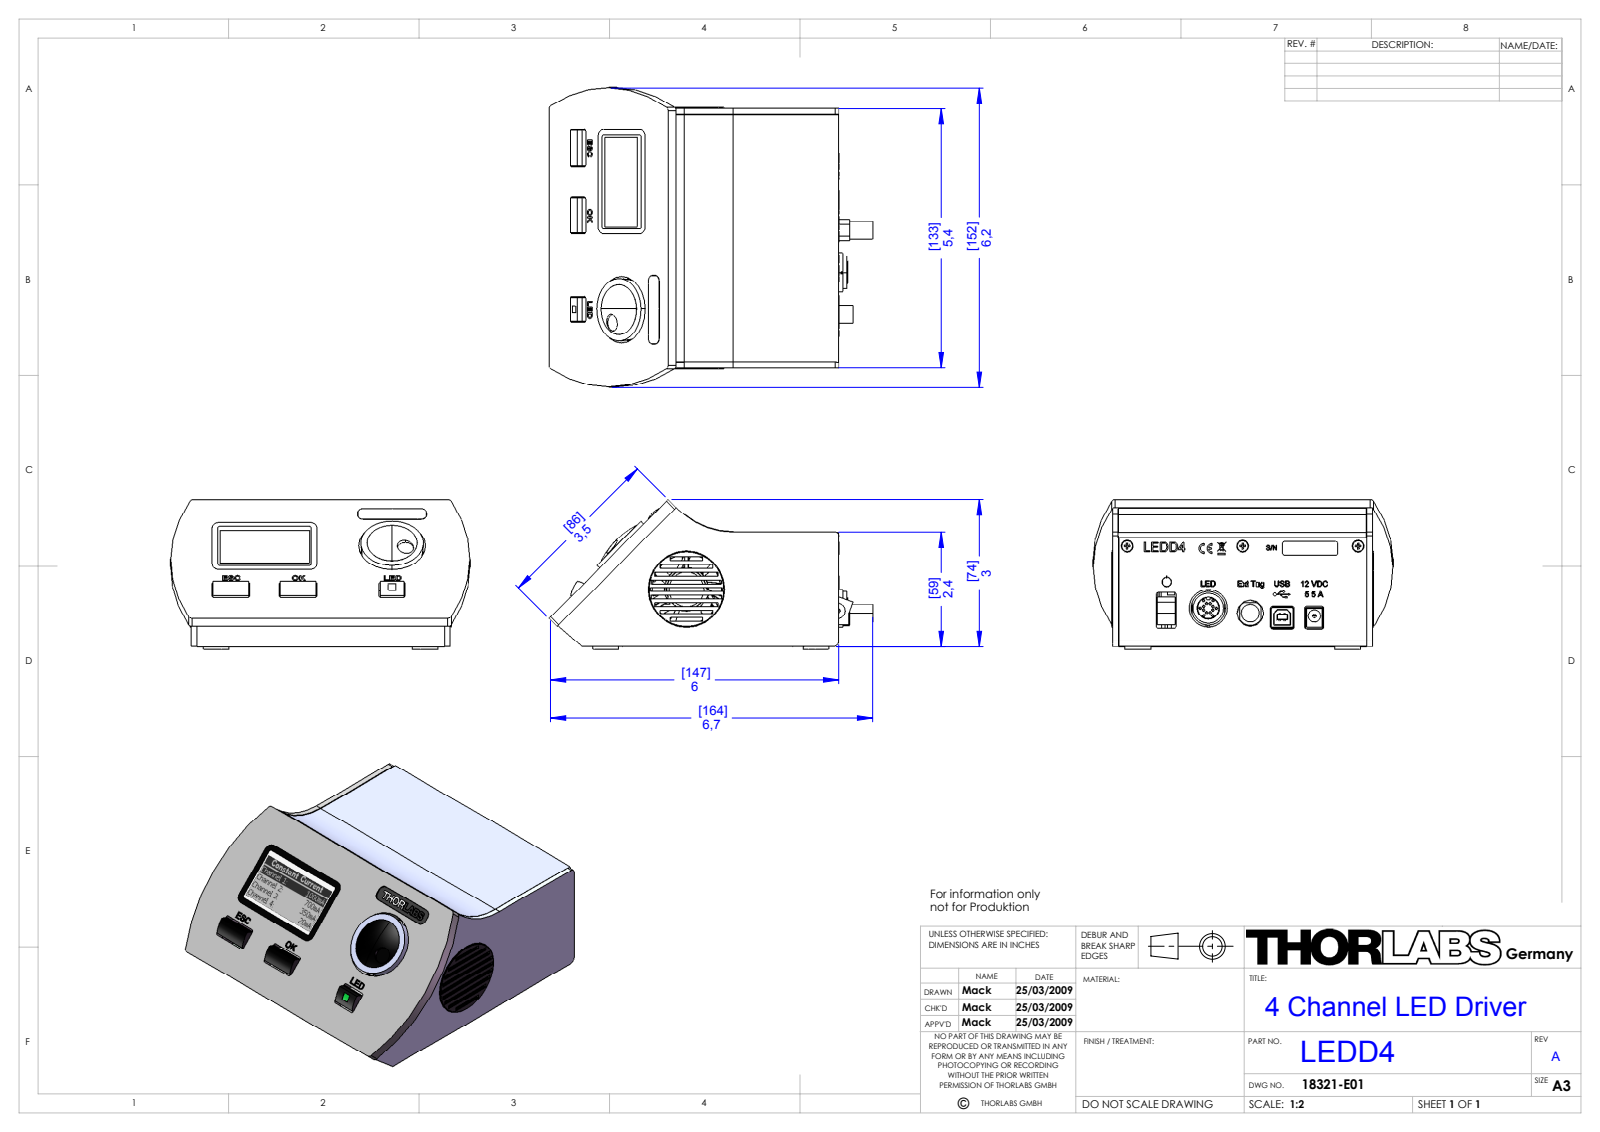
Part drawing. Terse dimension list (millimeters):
name: dc_gedreht2_Standard; ledd4 rückwand sn_Standard; USB 9x4mm2008_Standard; CE-Zeichen 5mm2008_Standard (+8 more)
written by: SolidWorks 2008 (AUTOMOTIVE_DESIGN)
unit: mm
bodies: 95 solids, 3611 faces (2464 planar, 682 cylindrical, 465 other)
size: 169.95 × 157.01 × 78.65
volume: 279 308 mm³; area: 216 111 mm²
holes: 14× ⌀0.6, 14× ⌀1, 10× ⌀6.2, 7× ⌀3.2, 7× ⌀3.9, 4× ⌀3, 4× ⌀3.5, 4× ⌀4, 4× ⌀4.3, 4× ⌀13, 2× ⌀0.89, 2× ⌀1.78
bosses: 14× ⌀0.7, 7× ⌀5.5, 7× ⌀3, 1× ⌀40, 1× ⌀36, 1× ⌀26.27, 1× ⌀23, 1× ⌀21
rounds: 57× R1, 20× R3, 12× R4, 11× R0.5, 9× R0.2, 9× R2, 8× R0.15, 8× R0.45
face distances: 3, 6, 56.8, 133, 53.8, 1.5, 2, 59.8, 136, 8
hole spacings: 121, 2.58, 3.65, 150.5, 1.9, 2.05, 2.08, 3.05
